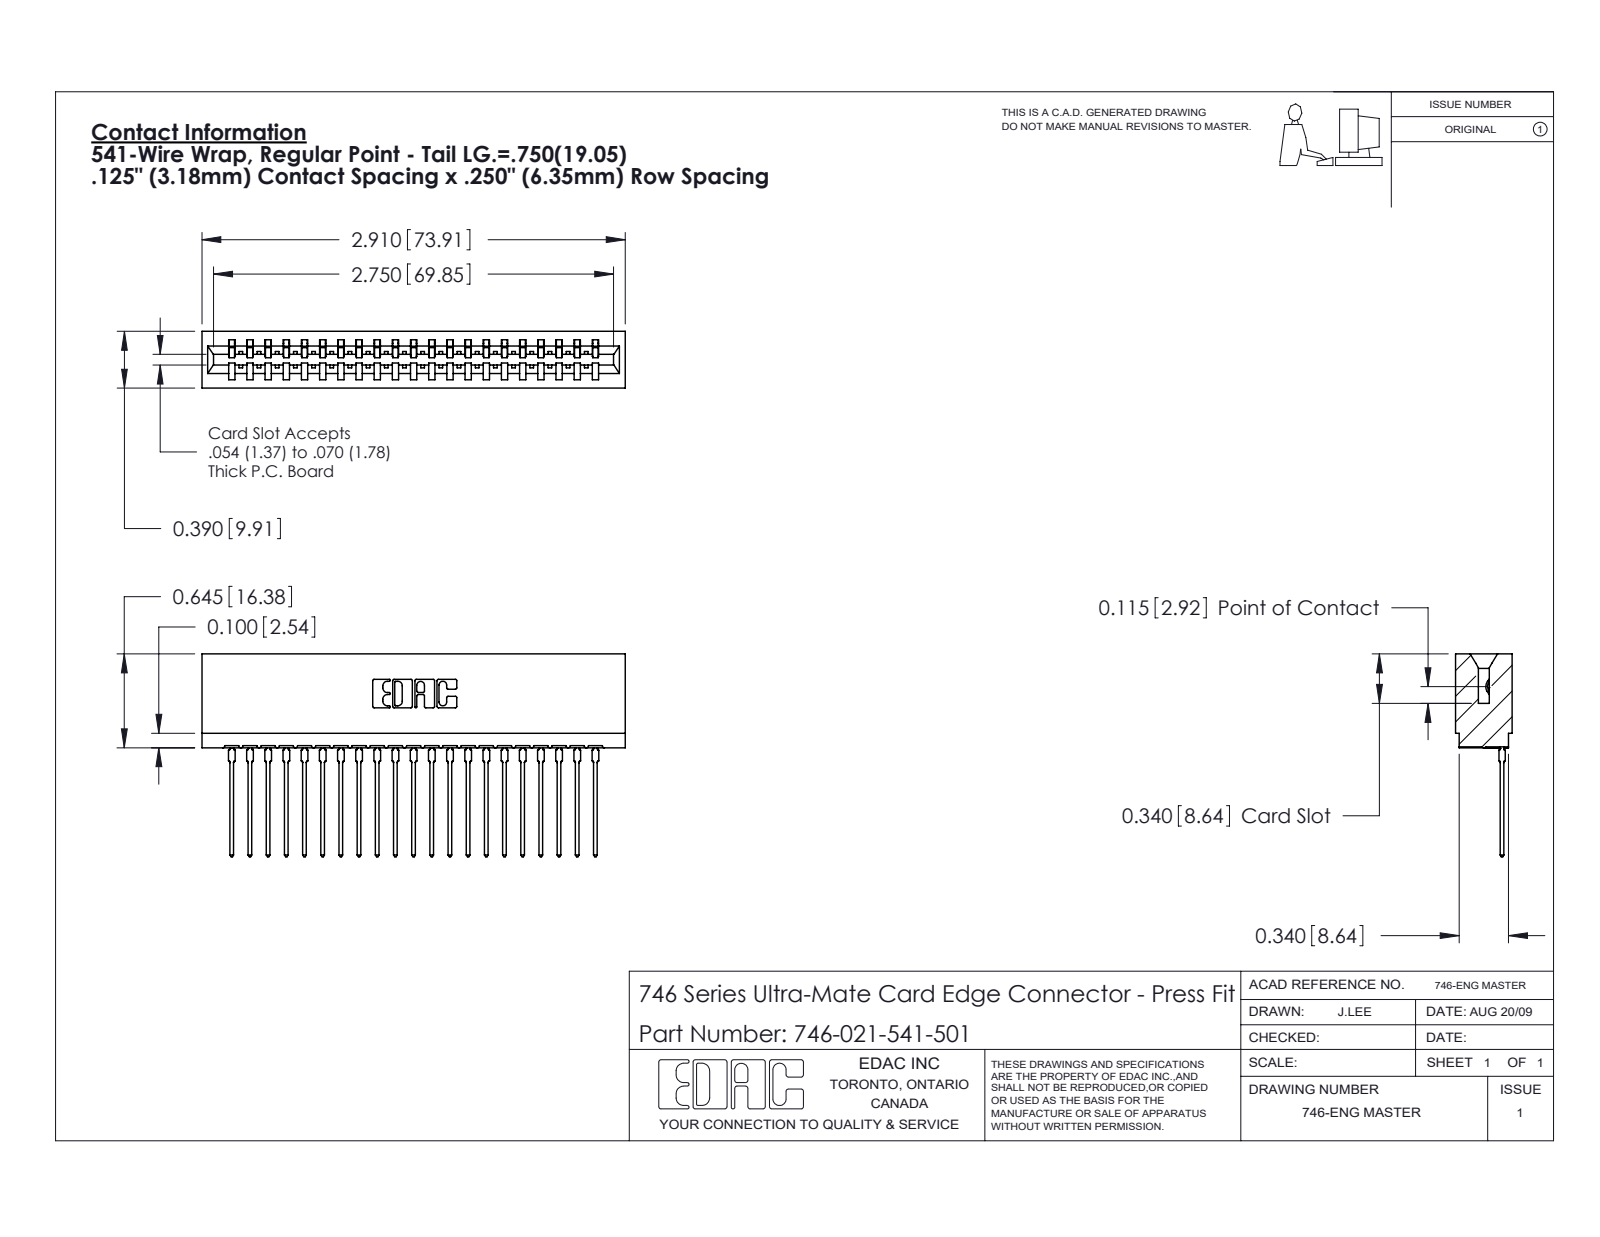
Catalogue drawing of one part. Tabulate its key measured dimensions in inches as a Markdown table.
| quantity | value |
| --- | --- |
| part name | 746-021-541-501; 746-292-001_541; 746 Part_.340 Slot Depth - 01 |
| STEP written by | SolidWorks 2020 (CONFIG_CONTROL_DESIGN) |
| units | inches |
| bodies | 22 solids, 2365 faces (1378 planar, 441 cylindrical, 546 other) |
| overall size | 2.91 × 1.394 × 0.39 |
| volume | 0.52 in³ |
| surface area | 18.13 in² |
| partial cylindrical surfaces (radius × count) | 0.021 × 42, 0.01 × 22, 0.015 × 22, 0.007 × 6, 0.031 × 6, 0.005 × 4, 0.011 × 4, 0.026 × 3 |
| main face-to-face distances | 0.25, 0.057, 0.333, 0.39, 0.5, 0.025, 0.307, 0.083, 0.125, 0.292 |
